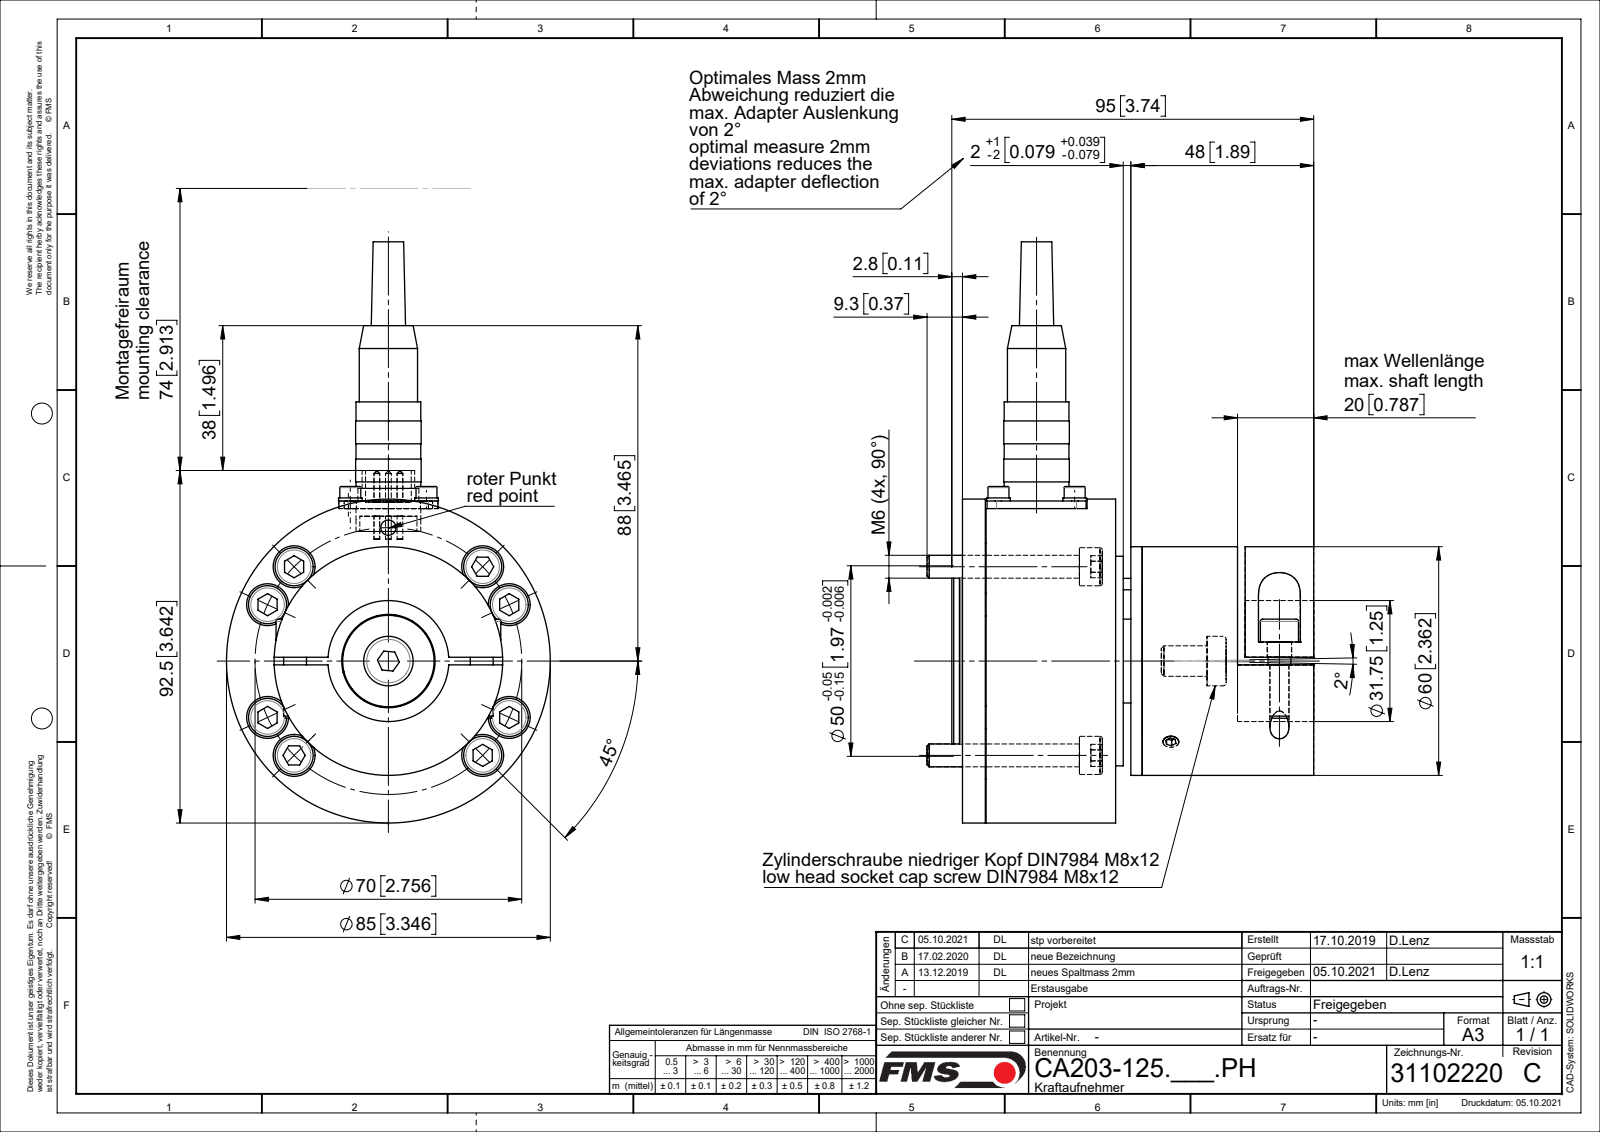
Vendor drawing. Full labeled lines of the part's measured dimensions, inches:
Part name (STEP PRODUCT): Zyl-Schr DIN912_M6x40; RKL_6203_01; 070907-4_01; 31102203_01 (+8 more)
STEP written by: SolidWorks 2018 (CONFIG_CONTROL_DESIGN)
Units: inches
Bodies: 44 solids, 821 faces (294 planar, 332 cylindrical, 195 other)
Overall size (bounding box): 6.004 × 3.996 × 3.346
Volume: 18.12 in³ · Surface area: 170 in²
Round holes (diameter × count): ⌀0.098 ×8, ⌀0.256 ×8, ⌀0.433 ×8, ⌀0.197 ×6, ⌀0.157 ×5, ⌀0.122 ×4, ⌀0.126 ×4, ⌀0.142 ×4, ⌀0.276 ×4, ⌀0.252 ×2, ⌀0.118 ×1, ⌀0.165 ×1
Round bosses / shafts (diameter × count): ⌀0.236 ×11, ⌀0.394 ×10, ⌀0.118 ×8, ⌀0.059 ×5, ⌀0.244 ×4, ⌀0.224 ×4, ⌀0.217 ×4, ⌀3.346 ×1
Partial cylindrical surfaces — rounded edges, fillets, slot ends (radius × count): R0.098 ×4, R0.197 ×2, R0.217 ×2
Main face-to-face distances: 0.079, 1.614, 1.181, 0.236, 1.772, 0.394, 1.969, 0.118, 1.339, 0.472
Hole centre spacings: 1.378, 0.787, 0.976, 0.992, 1.291, 2.013, 2.223, 1.113
